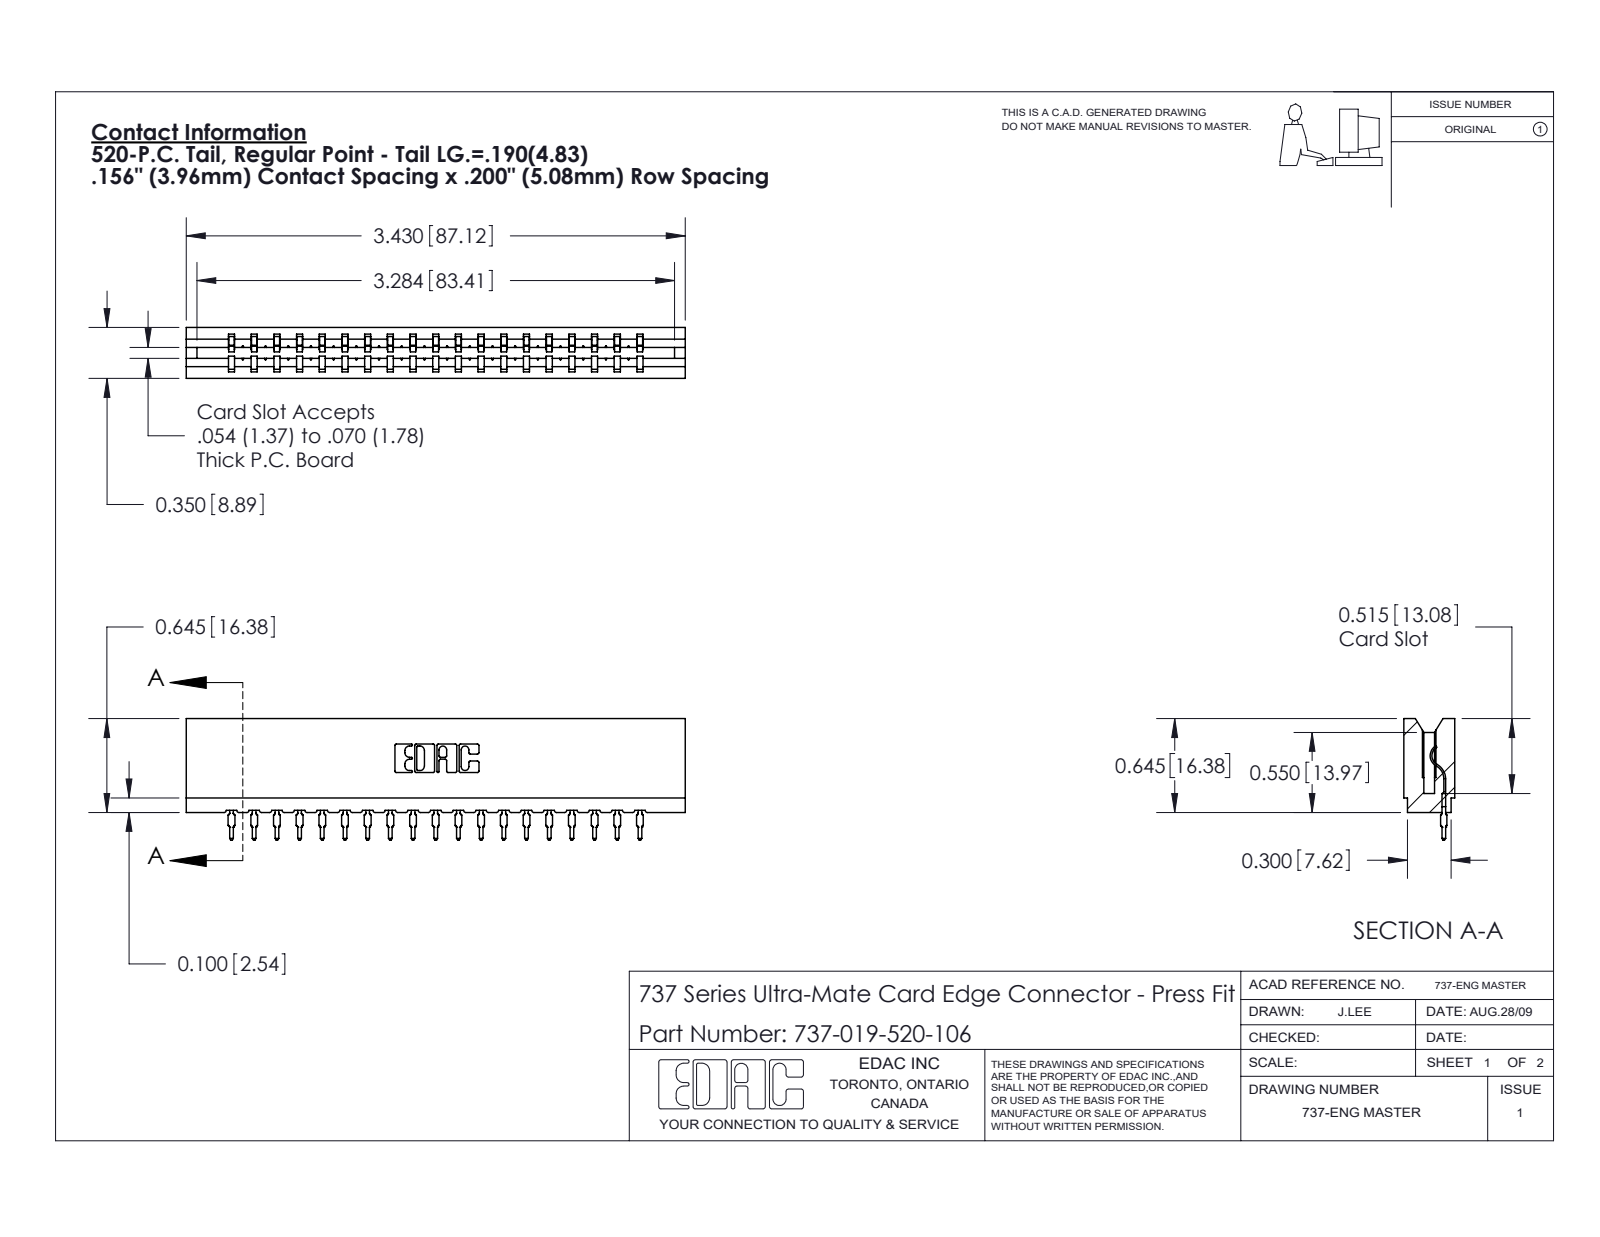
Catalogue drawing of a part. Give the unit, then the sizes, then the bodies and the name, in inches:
Units: inches
Overall size (bounding box): 3.43 × 0.836 × 0.35
Partial cylindrical surfaces — rounded edges, fillets, slot ends (radius × count): R0.015 ×38, R0.021 ×38, R0.01 ×22, R0.007 ×6, R0.031 ×6, R0.005 ×4, R0.011 ×4, R0.026 ×3
Main face-to-face distances: 0.138, 0.212, 0.35, 0.156, 0.624, 0.468, 0.78, 0.074, 1.404, 0.312
Volume: 0.521 in³ · Surface area: 16.93 in²
Bodies: 20 solids, 2242 faces (1347 planar, 401 cylindrical, 494 other)
Part name (STEP PRODUCT): 745-292-001_520; 737 Part_Insulator Option - 06; 737-019-520-106
STEP written by: SolidWorks 2020 (CONFIG_CONTROL_DESIGN)
